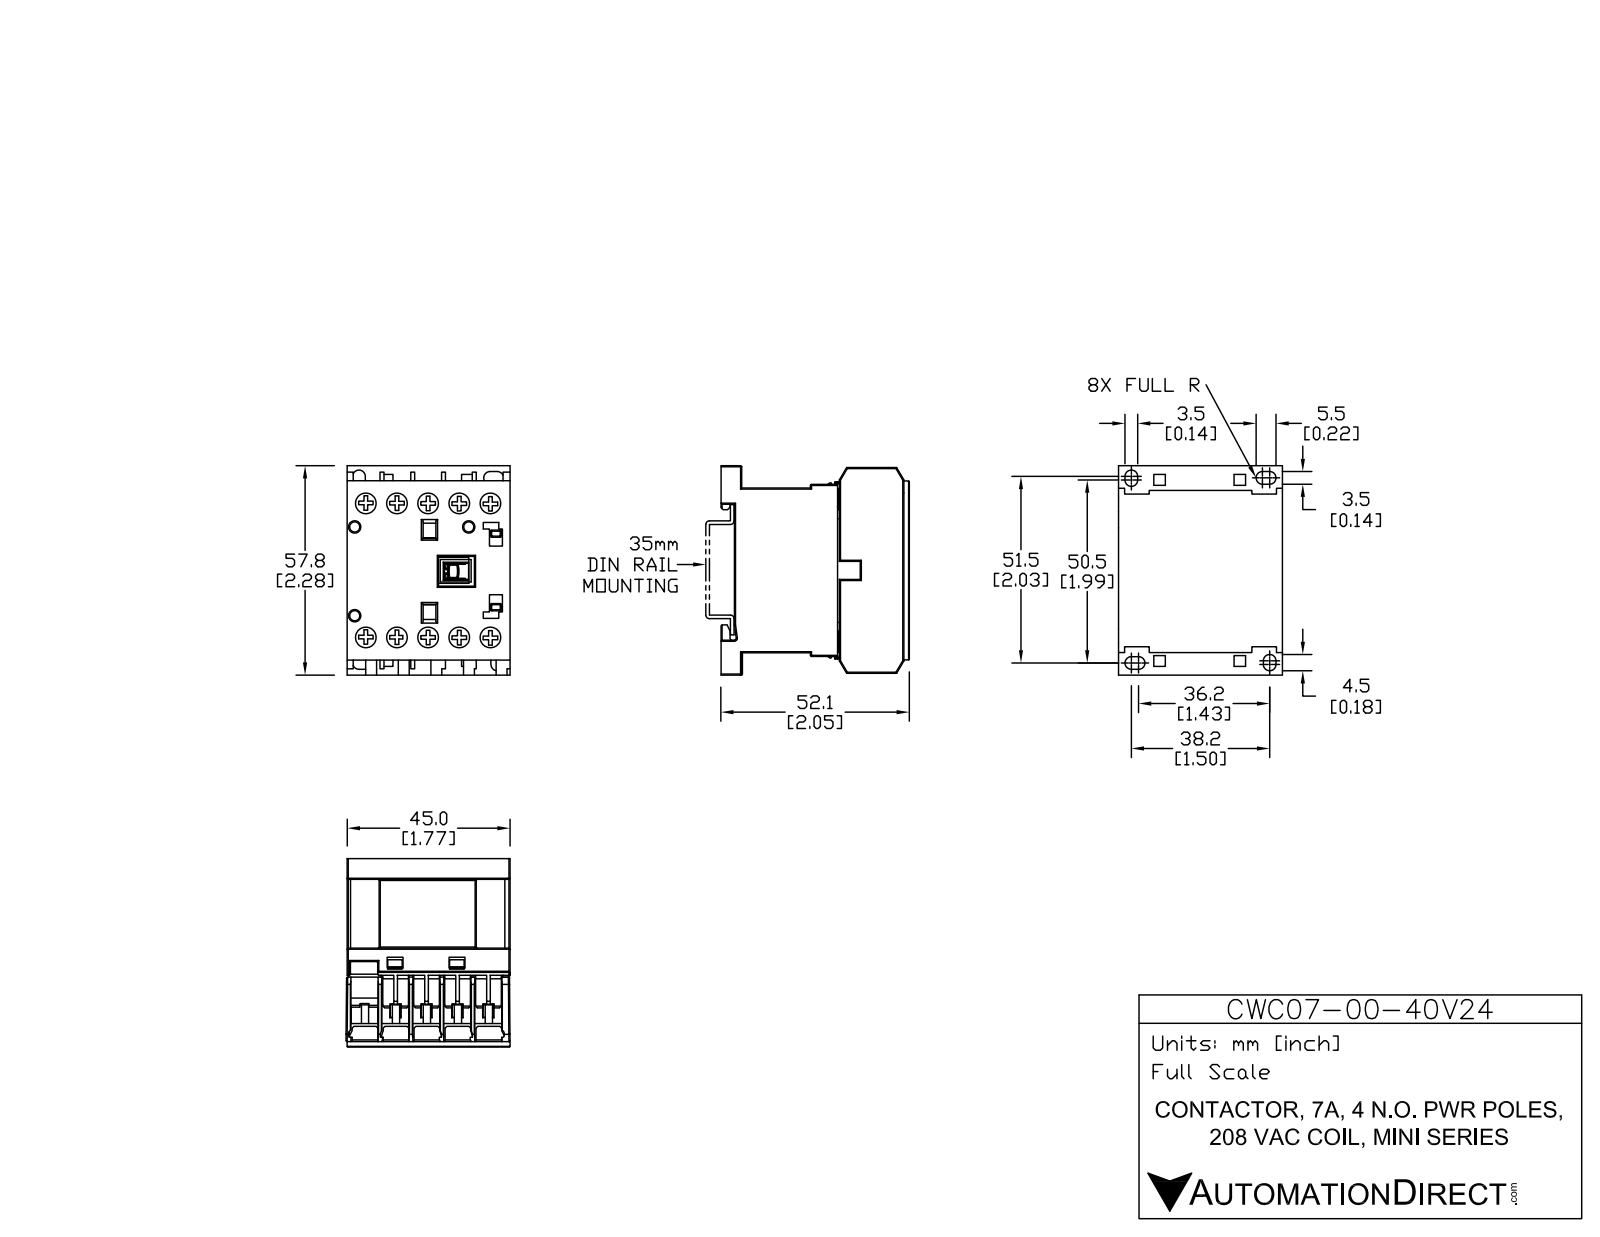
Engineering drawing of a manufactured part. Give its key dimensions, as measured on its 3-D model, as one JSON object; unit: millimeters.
{"part_name": "CWC07-00-40V24", "step_written_by": "SolidWorks 2013 (AUTOMOTIVE_DESIGN)", "units": "millimeters", "bodies": {"solids": 15, "faces": 535, "planar": 445, "cylindrical": 90, "other": 0}, "overall_size": [58.04, 52.12, 45.75], "volume_mm3": 97133, "surface_area_mm2": 30437, "round_holes": [[6.2, 10], [2.8, 3]], "round_bosses_or_shafts": [[5.9, 10]], "partial_cylinders_radius": [[0.3, 20], [1.72, 6], [1.73, 2], [0.32, 1], [0.42, 1], [0.55, 1]], "face_to_face_distances": [8.25, 45.5, 1.25, 16.5, 9.5, 5.5, 17.75, 5.13, 10.63, 7], "hole_center_spacings": [8.55, 37.94, 17.1, 40.72, 36.96, 25.65, 44.99, 6.91]}
